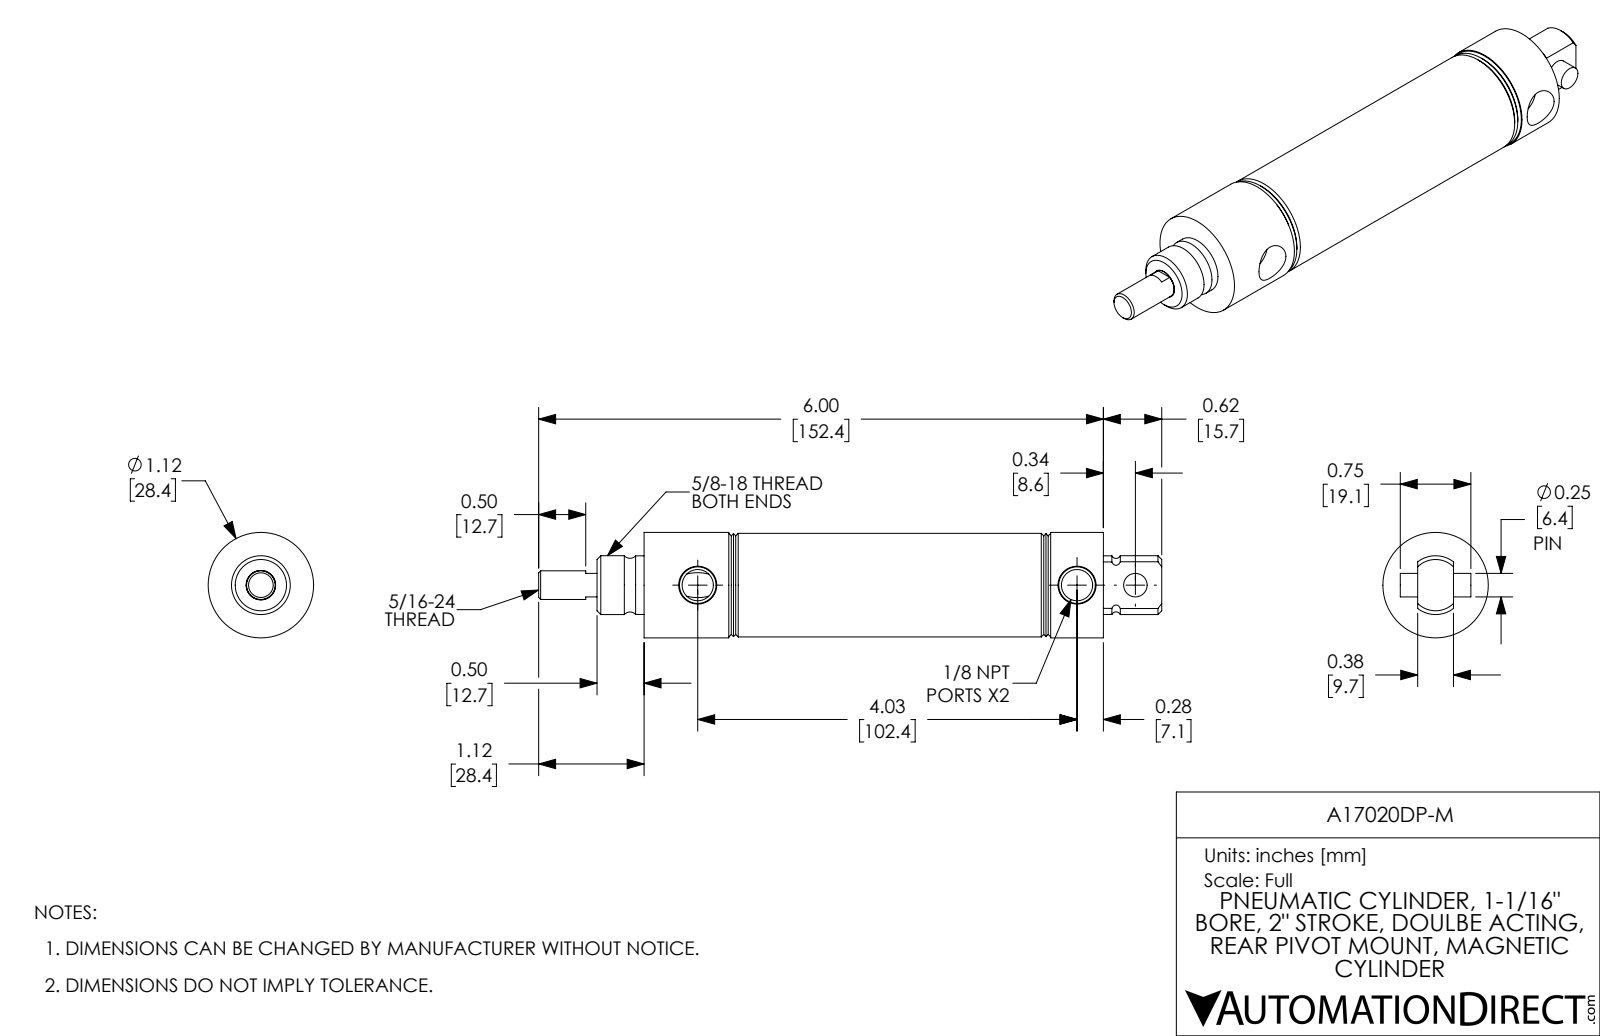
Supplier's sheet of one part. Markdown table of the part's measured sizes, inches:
| quantity | value |
| --- | --- |
| part name | A17020DP-M-PIN; A17020DP-M-Rod; A17020DP-M-MainBody; A17020DP-M |
| STEP written by | SolidWorks 2017 (AUTOMOTIVE_DESIGN) |
| units | inches |
| bodies | 3 solids, 92 faces (22 planar, 32 cylindrical, 38 other) |
| overall size | 6.62 × 1.12 × 1.12 |
| volume | 3.306 in³ |
| surface area | 42.31 in² |
| round holes (diameter × count) | 0.332 × 2, 0.25 × 1, 0.312 × 1, 1.063 × 1 |
| round bosses / shafts (diameter × count) | 1.12 × 1, 1.1 × 1, 0.625 × 1, 0.623 × 1, 0.304 × 1 |
| partial cylindrical surfaces (radius × count) | 0.313 × 1 |
| main face-to-face distances | 0.5, 3.69, 2.5, 2, 1.19, 1.69, 3.69, 4.88, 3.19, 1.19 |
| hole center spacings | 0.62, 4.03, 4.65 |
